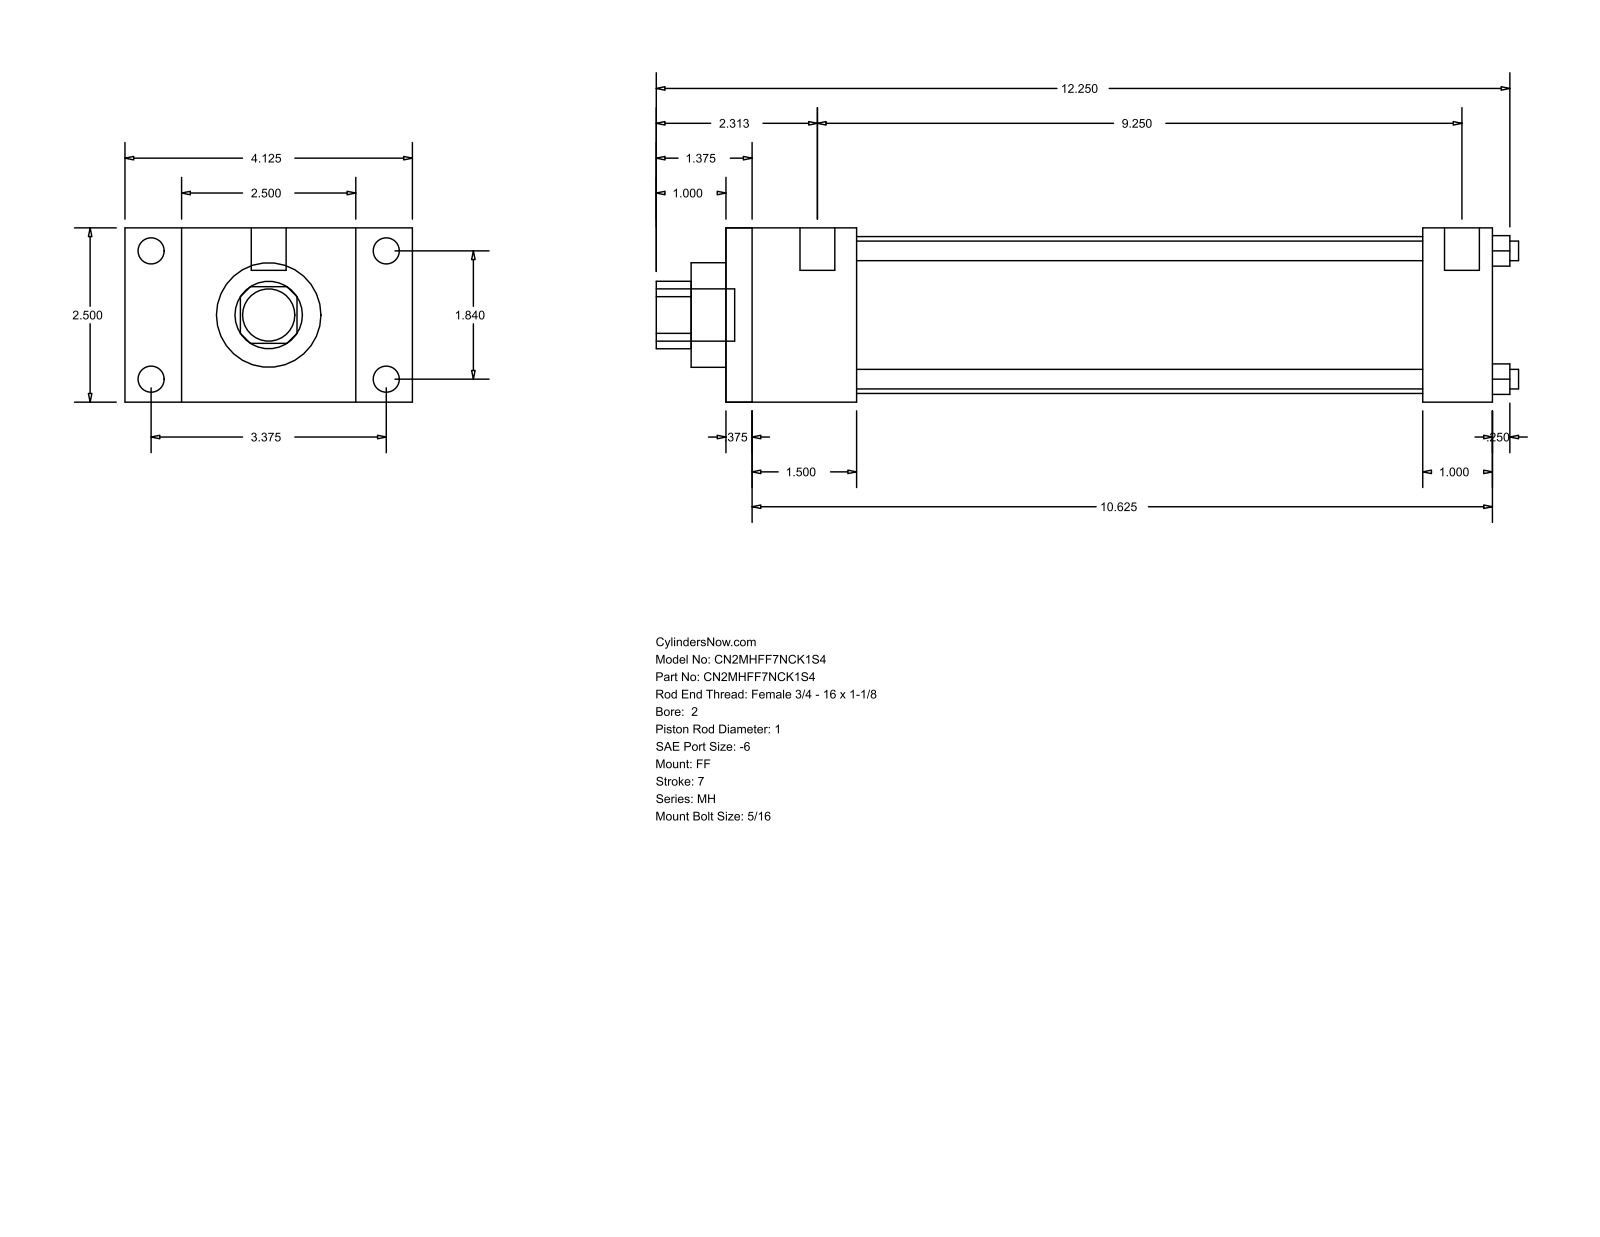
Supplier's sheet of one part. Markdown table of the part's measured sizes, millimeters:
| quantity | value |
| --- | --- |
| part name | MH_FF__0200_1 |
| STEP written by | GSSL Pune (CONFIG_CONTROL_DESIGN) |
| units | millimeters |
| bodies | 0 solids, 92 faces (64 planar, 28 cylindrical, 0 other) |
| overall size | 314.32 × 104.78 × 63.5 |
| round holes (diameter × count) | 7.14 × 4, 25.4 × 1, 38.1 × 1, 57.15 × 1 |
| round bosses / shafts (diameter × count) | 9.53 × 4, 5.56 × 4, 12.7 × 2, 19.05 × 1 |
| partial cylindrical surfaces (radius × count) | 12.29 × 1 |
| main face-to-face distances | 63.5, 279.4, 9.52, 269.88, 20.64, 25.4, 47.63, 254, 38.11, 244.48 |
| hole center spacings | 33.05, 46.74, 66.1 |
